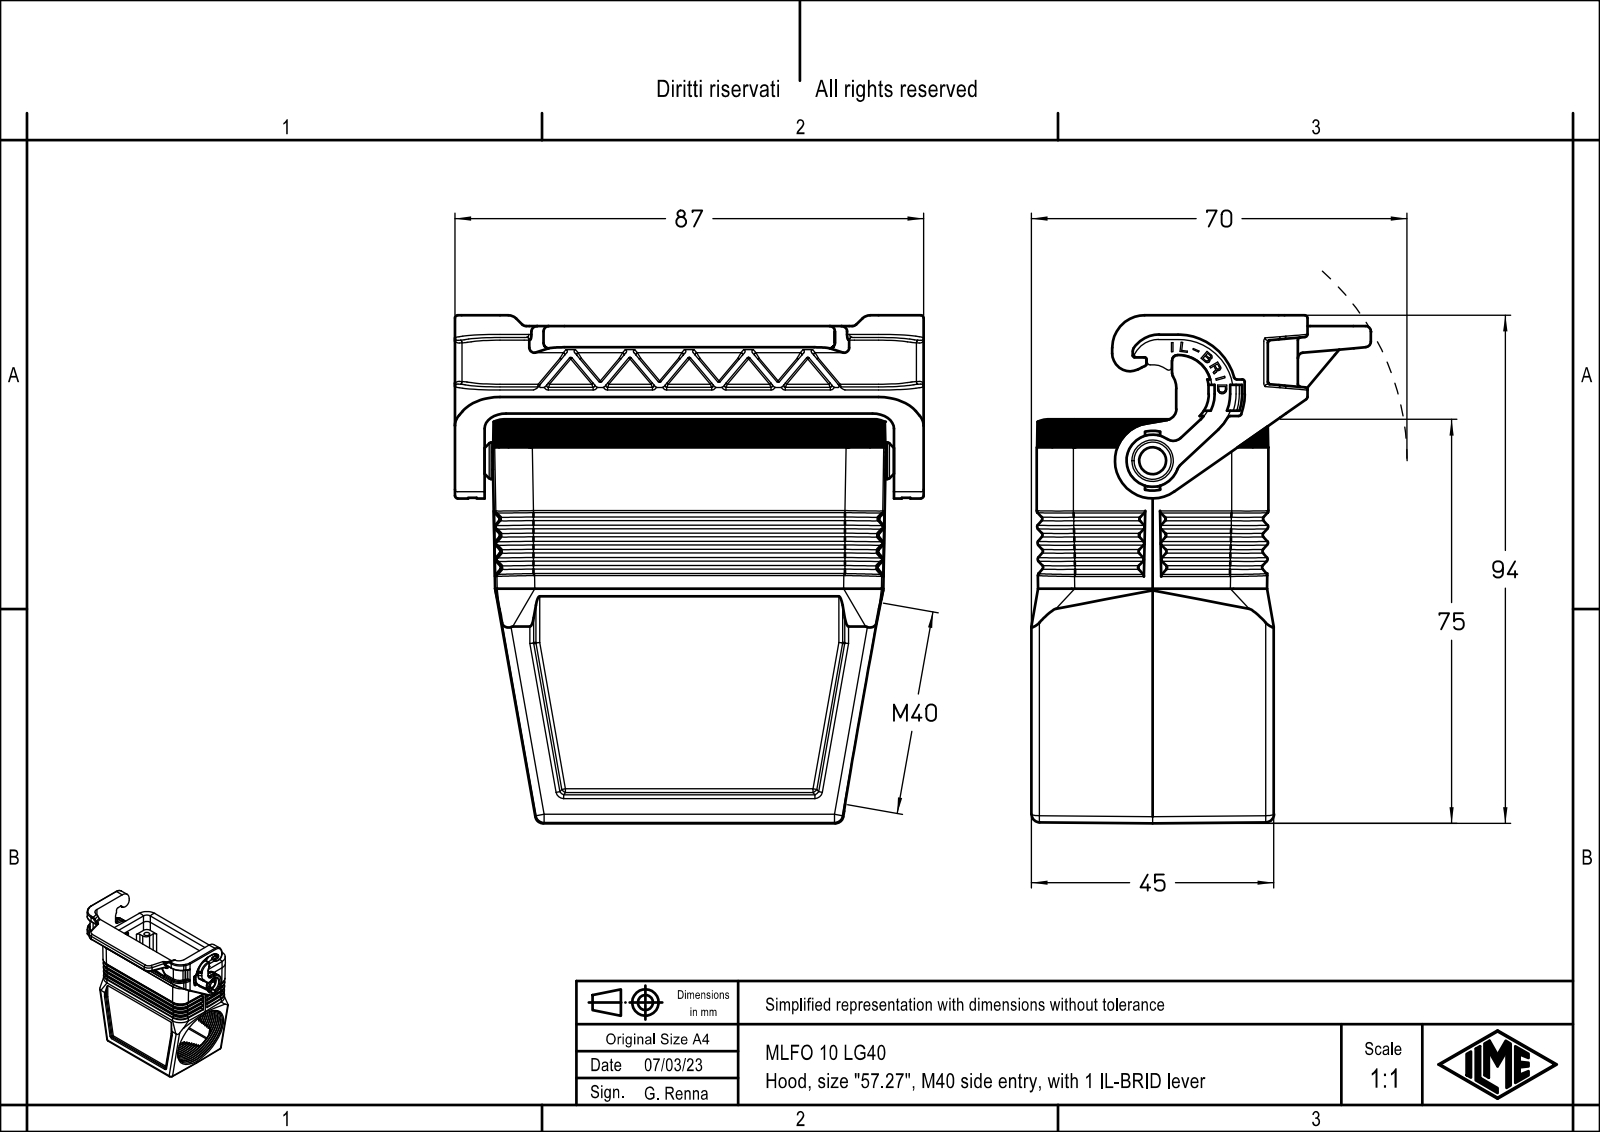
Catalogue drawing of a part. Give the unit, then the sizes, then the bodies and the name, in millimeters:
Units: millimetres
Overall size (bounding box): 94.25 × 87 × 63
Round holes (diameter × count): ⌀3 ×4, ⌀3.5 ×4, ⌀3.25 ×1, ⌀5.4 ×1, ⌀7.7 ×1
Round bosses / shafts (diameter × count): ⌀6.9 ×1, ⌀6.8 ×1, ⌀5.2 ×1, ⌀3.2 ×1
Partial cylindrical surfaces — rounded edges, fillets, slot ends (radius × count): R0.1 ×27, R0.5 ×25, R1.5 ×25, R0.2 ×15, R1 ×14, R7 ×14, R0.33 ×13, R3 ×12
Main face-to-face distances: 39.25, 3.75, 43, 1, 4.75, 7, 35.5, 34.5, 38.25, 2
Hole centre spacings: 27, 57, 63.07
Volume: 81 890 mm³ · Surface area: 45 724 mm²
Bodies: 1 solid, 1289 faces (713 planar, 305 cylindrical, 271 other)
Part name (STEP PRODUCT): MLFO 10 LG40
STEP written by: Creo Elements/Direct Modeling 20.1B 02-Apr-2019 (C) Parametric Technology GmbH (AUTOMOTIVE_DESIGN)
